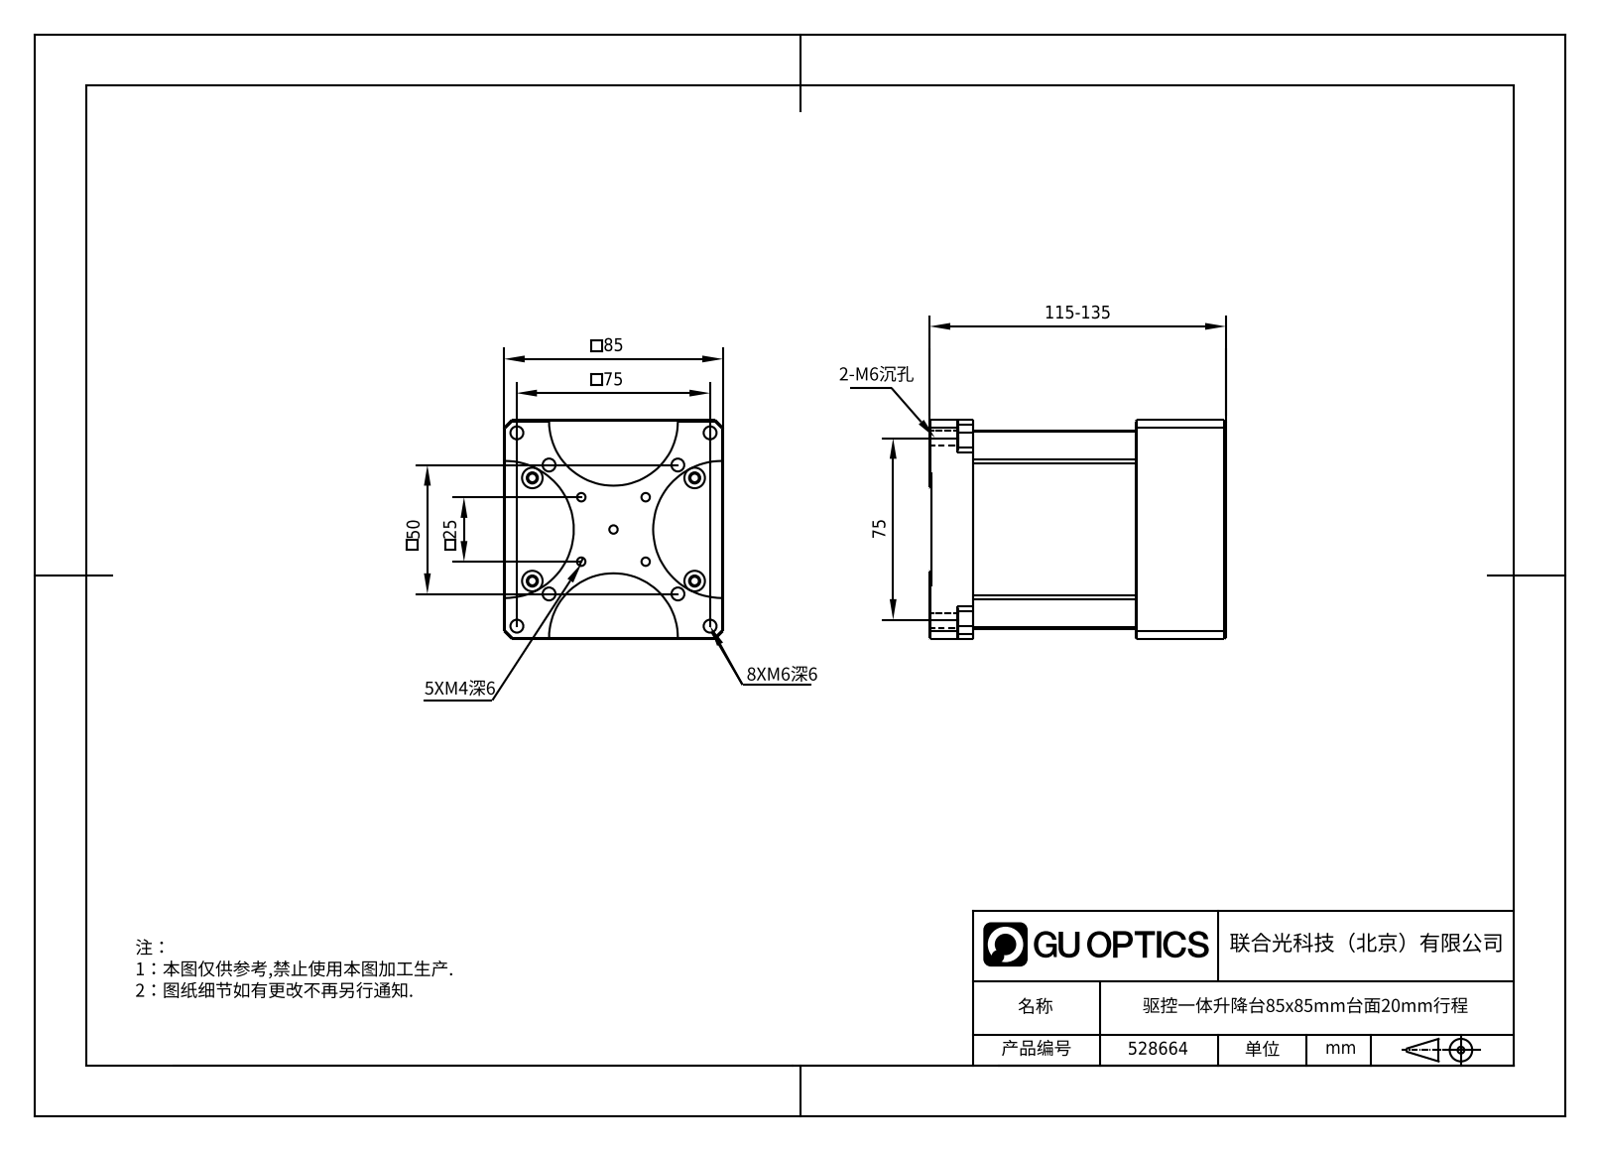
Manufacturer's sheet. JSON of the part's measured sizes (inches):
{"part_name": "528664", "step_written_by": "SolidWorks 2020 (CONFIG_CONTROL_DESIGN)", "units": "inches", "bodies": {"solids": 28, "faces": 2354, "planar": 1233, "cylindrical": 677, "other": 444}, "overall_size": [4.763, 3.673, 3.346], "volume_in3": 33.95, "surface_area_in2": 316.7, "round_holes": [[0.13, 23], [0.173, 20], [0.059, 18], [0.1, 12], [0.169, 12], [0.256, 12], [0.315, 12], [0.087, 8], [0.197, 8], [0.063, 6], [0.094, 6], [0.098, 6]], "round_bosses_or_shafts": [[0.079, 32], [0.866, 1], [0.472, 1], [0.236, 1]], "partial_cylinders_radius": [[0.079, 40], [0.098, 13], [0.118, 13], [0.157, 9], [0.236, 8], [0.039, 6], [0.226, 4], [0.087, 3]], "face_to_face_distances": [0.138, 0.295, 0.157, 0.02, 0.276, 0.256, 3.051, 3.189, 2.205, 2.756], "hole_center_spacings": [0.591, 1.181, 0.547, 2.33, 1.22, 1.569, 0.354, 0.709]}
